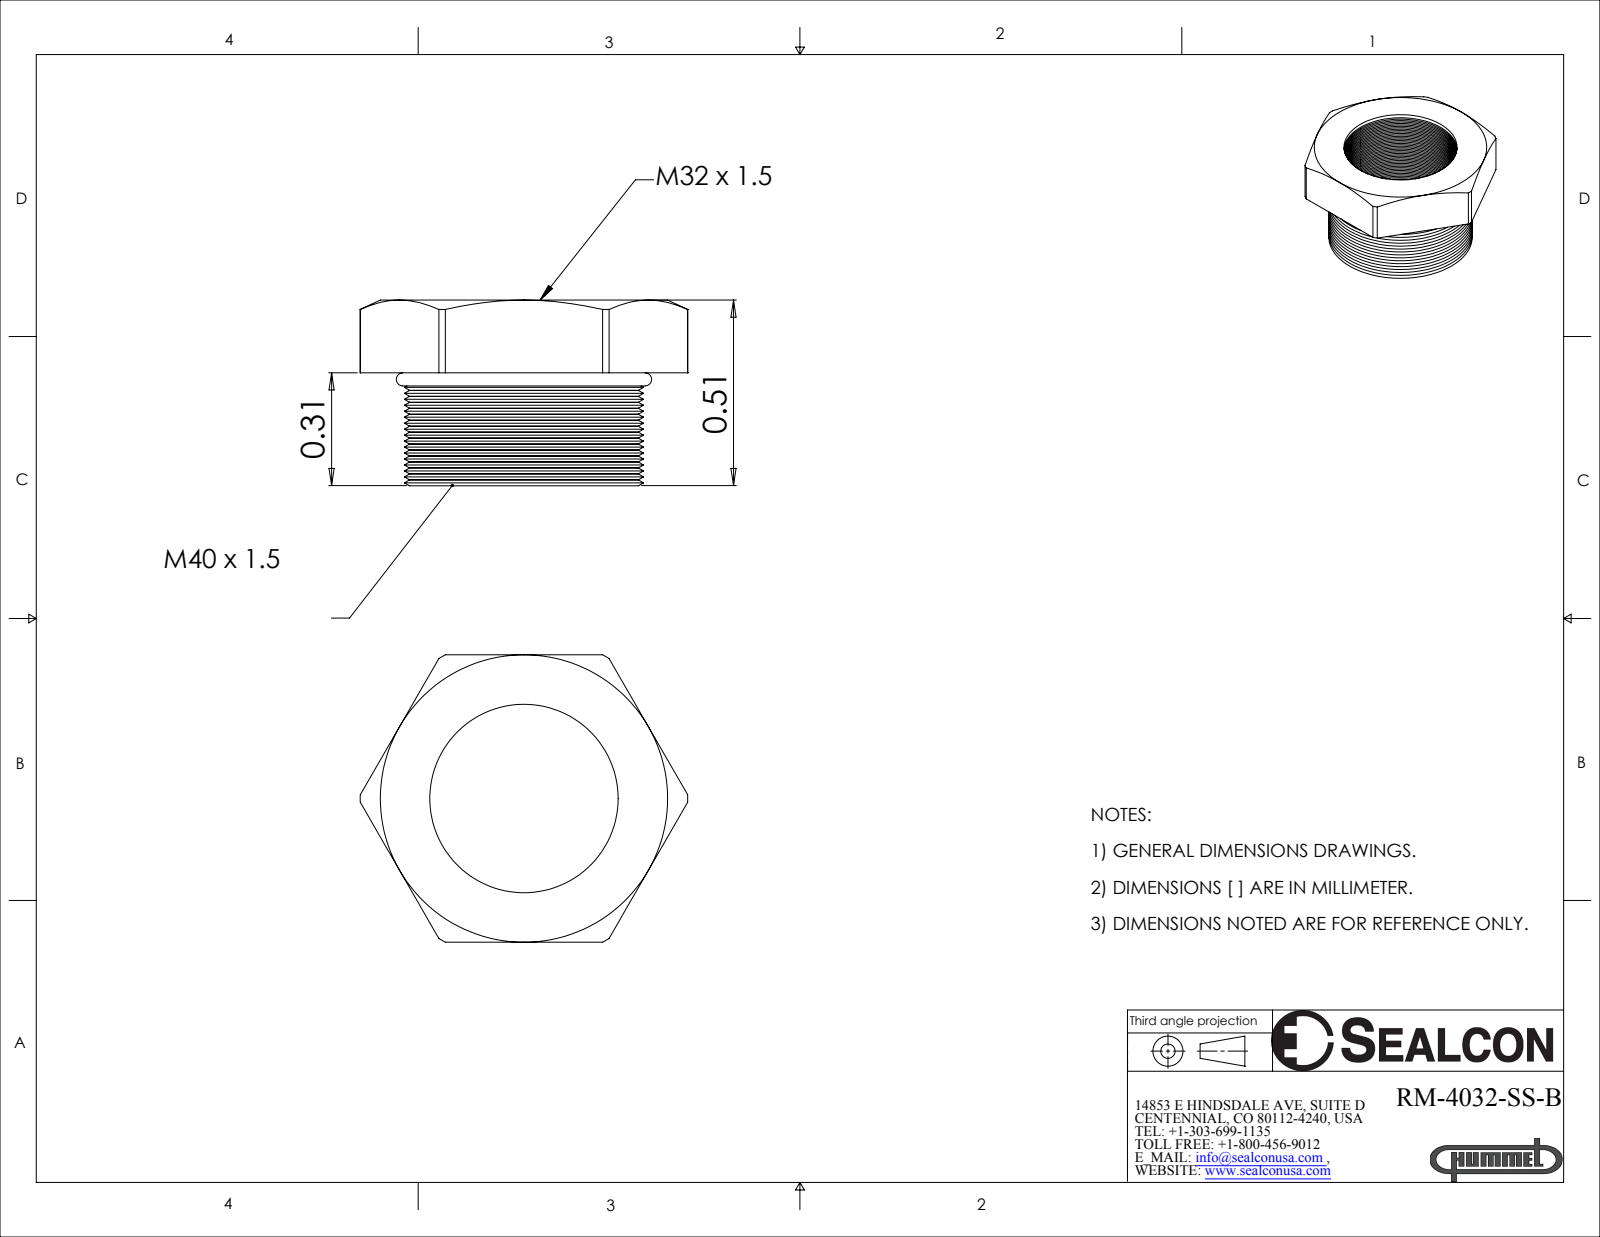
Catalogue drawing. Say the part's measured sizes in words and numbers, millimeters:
The part is named "RM-4032-SS-B". Its 3-D file was written by "SolidWorks 2008 (CONFIG_CONTROL_DESIGN)". It is 2 solids with 313 faces: 9 planar, 105 cylindrical and 199 other. Overall it measures 22.9 by 20.1 by 12.4 millimeters. Its volume is 1 500 cubic millimeters and its surface area 2 681 square millimeters. Round holes: 1 of diameter 13.2. Round bosses or shafts: 1 of diameter 16. Partial cylindrical surfaces (rounded edges, fillets, slot ends): 1 of radius 11.4. The main face-to-face distances are 4.6, 20.1, 7.9, 12.4.
